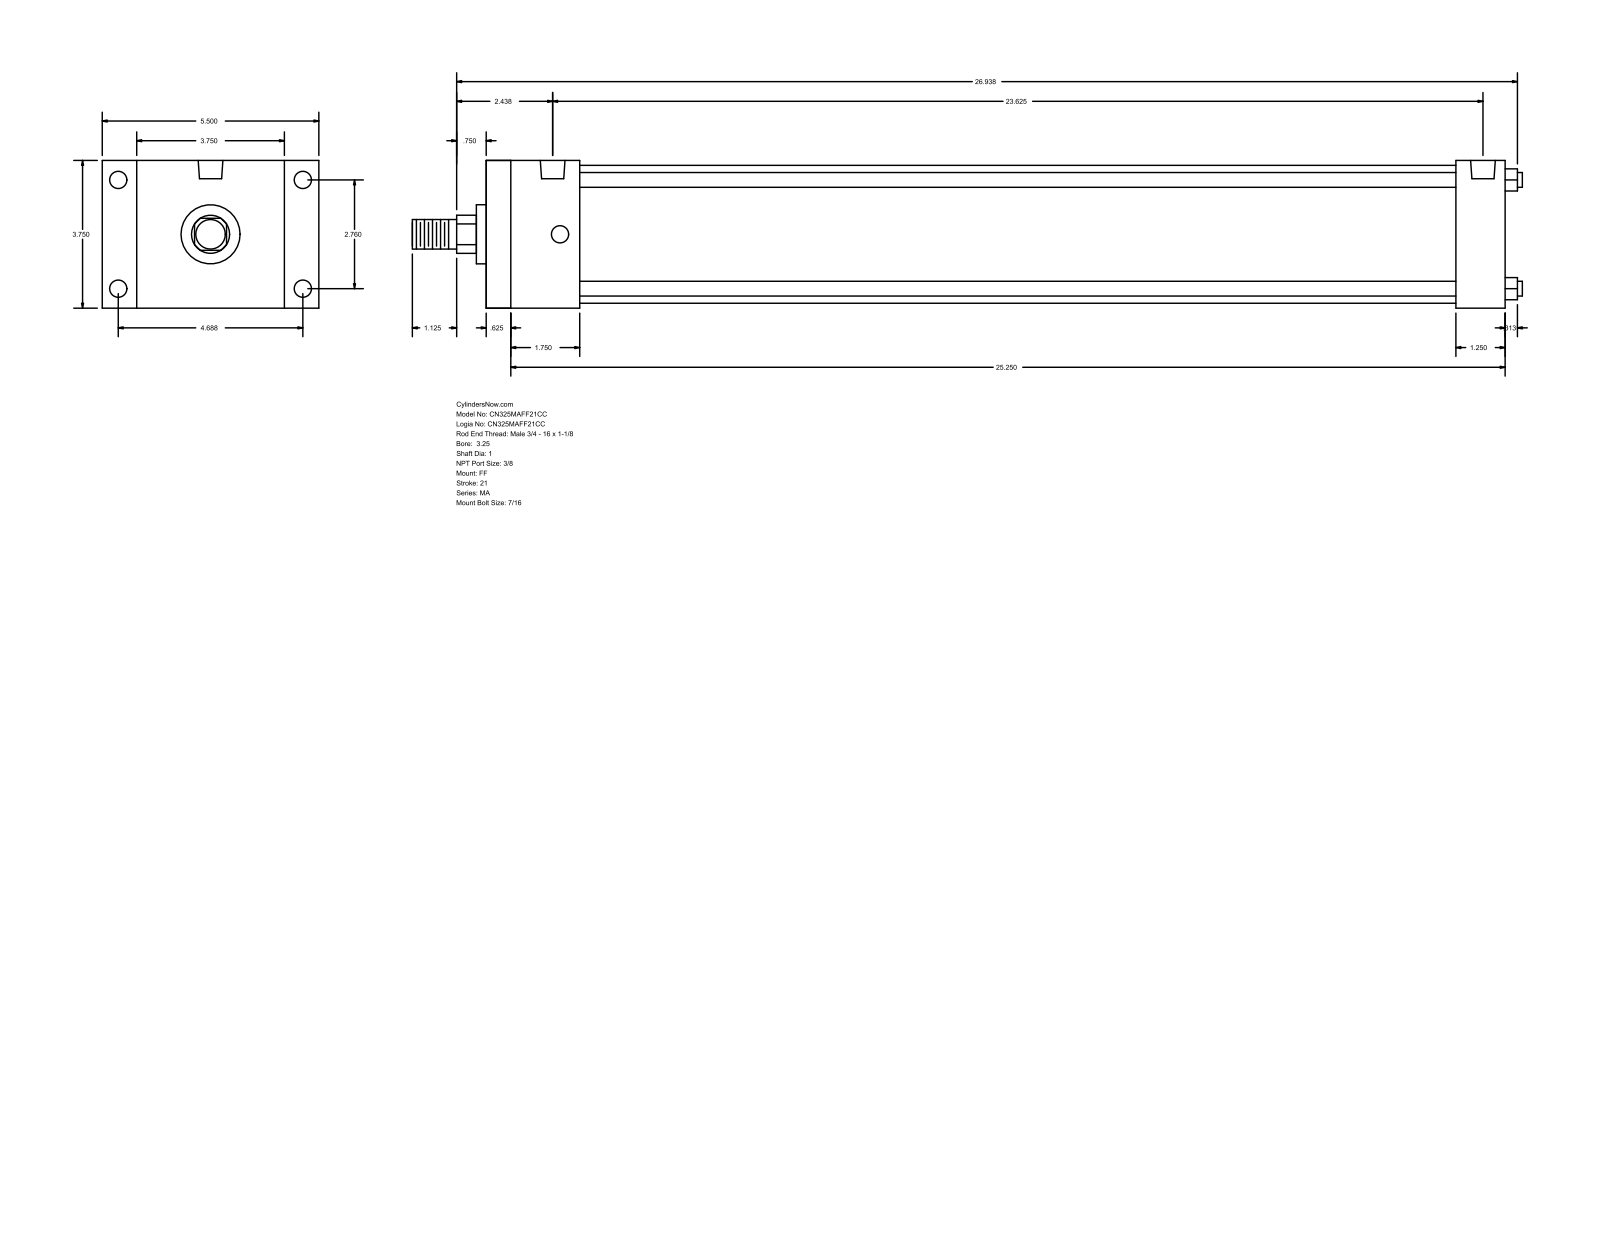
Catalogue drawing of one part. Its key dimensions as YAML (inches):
part_name: "MA_FF__0325_1"
step_written_by: "GSSL Pune (CONFIG_CONTROL_DESIGN)"
units: inches
bodies: {solids: 0, faces: 92, planar: 64, cylindrical: 28, other: 0}
overall_size: [28.187, 5.5, 3.75]
round_holes:
  - {diameter: 0.437, count: 8}
  - {diameter: 0.627, count: 2}
round_bosses_or_shafts:
  - {diameter: 0.375, count: 4}
  - {diameter: 3.5, count: 1}
  - {diameter: 1.5, count: 1}
  - {diameter: 1, count: 1}
  - {diameter: 0.75, count: 1}
partial_cylinders:
  - {radius: 0.484, count: 1}
face_to_face_distances: [3.75, 25.875, 0.625, 25.25, 0.875, 4.625, 2.375, 24.625, 1.75, 24]
hole_center_spacings: [0.187, 2.76, 4.687, 5.439, 23.25, 23.438, 23.625]
